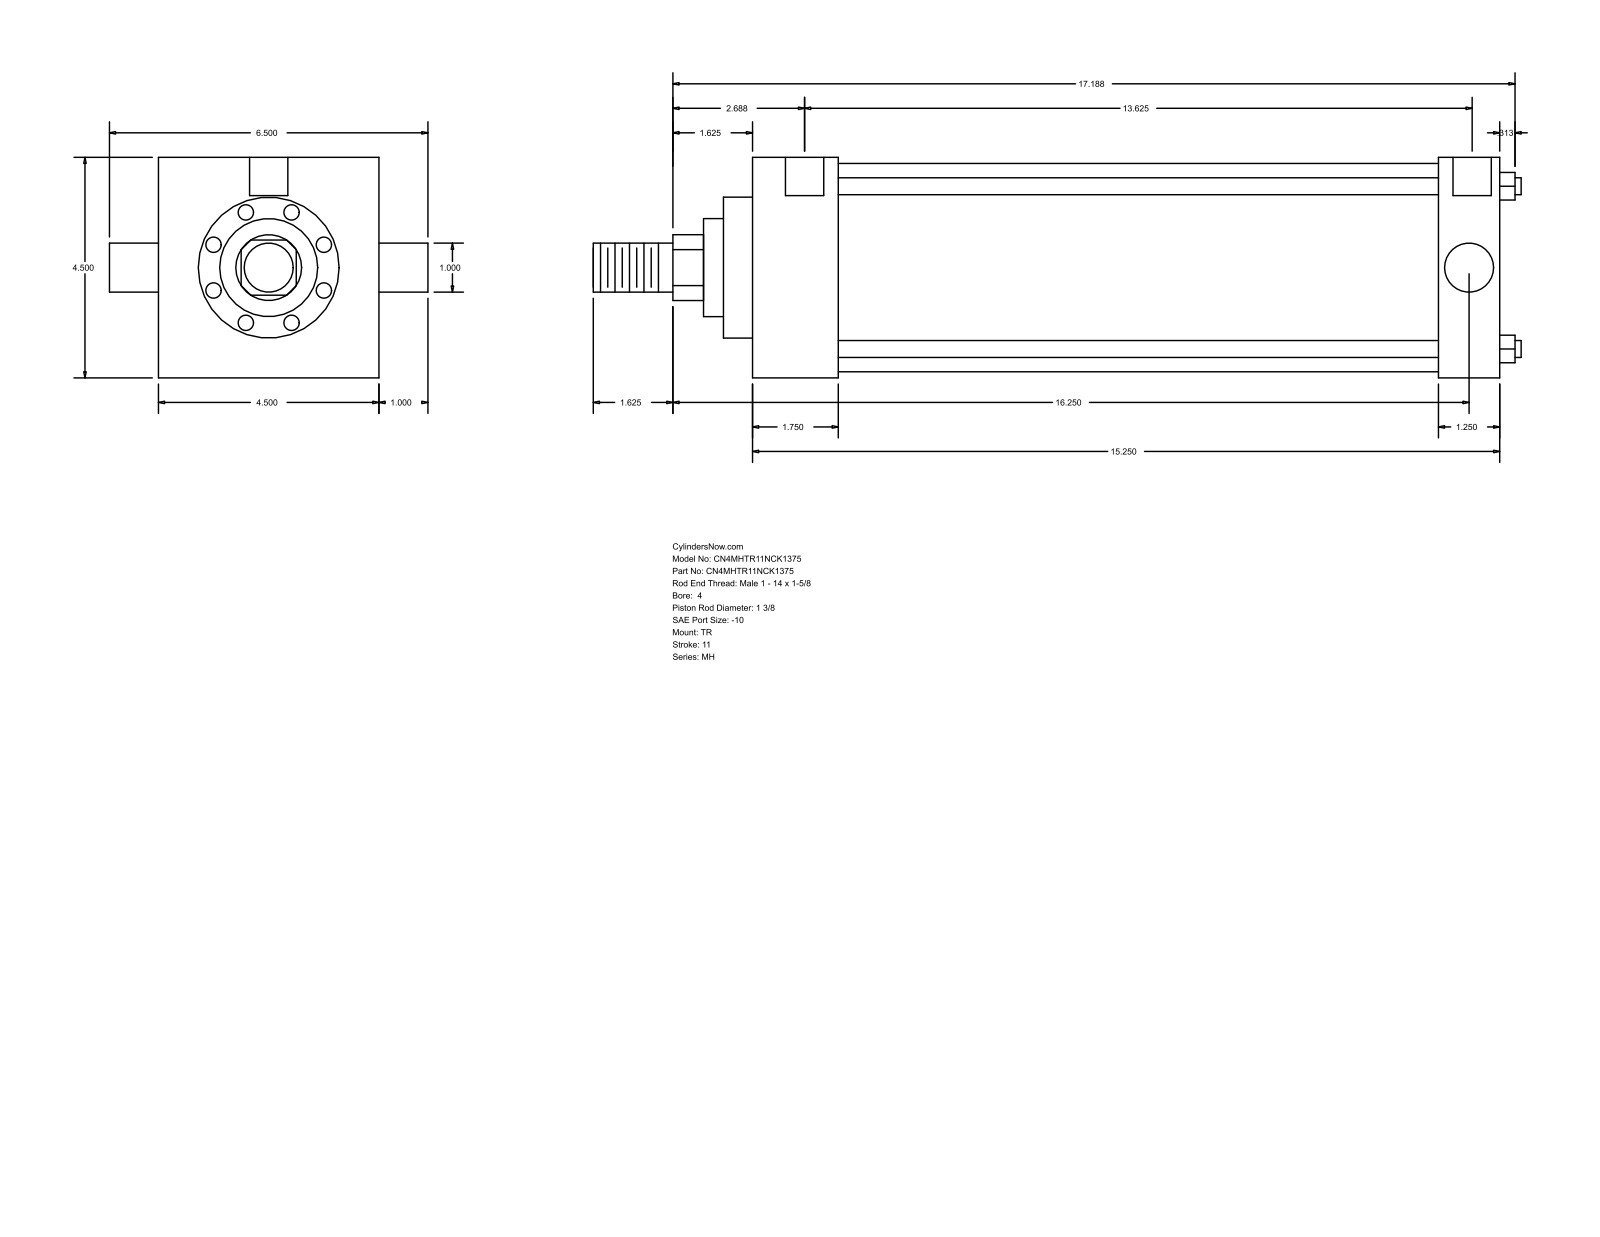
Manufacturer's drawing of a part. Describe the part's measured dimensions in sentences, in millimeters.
The part is named "MH_TR__0400_1.375". Its 3-D file was written by "GSSL Pune (CONFIG_CONTROL_DESIGN)". It is 0 solids with 86 faces: 61 planar, 25 cylindrical and 0 other. Overall it measures 481.01 by 165.1 by 114.3 millimeters. Round holes: 3 of diameter 8.73, 2 of diameter 19.84. Round bosses or shafts: 4 of diameter 8.76, 2 of diameter 25.4, 1 of diameter 107.95, 1 of diameter 73.03, 1 of diameter 50.8, 1 of diameter 34.92. Partial cylindrical surfaces (rounded edges, fillets, slot ends): 1 of radius 17.06. The main face-to-face distances are 114.3, 387.35, 44.45, 342.9, 355.61, 311.16, 31.74, 15.08, 59.53, 370.69. The hole center spacings are 1.59, 347.67, 346.08, 349.26.
